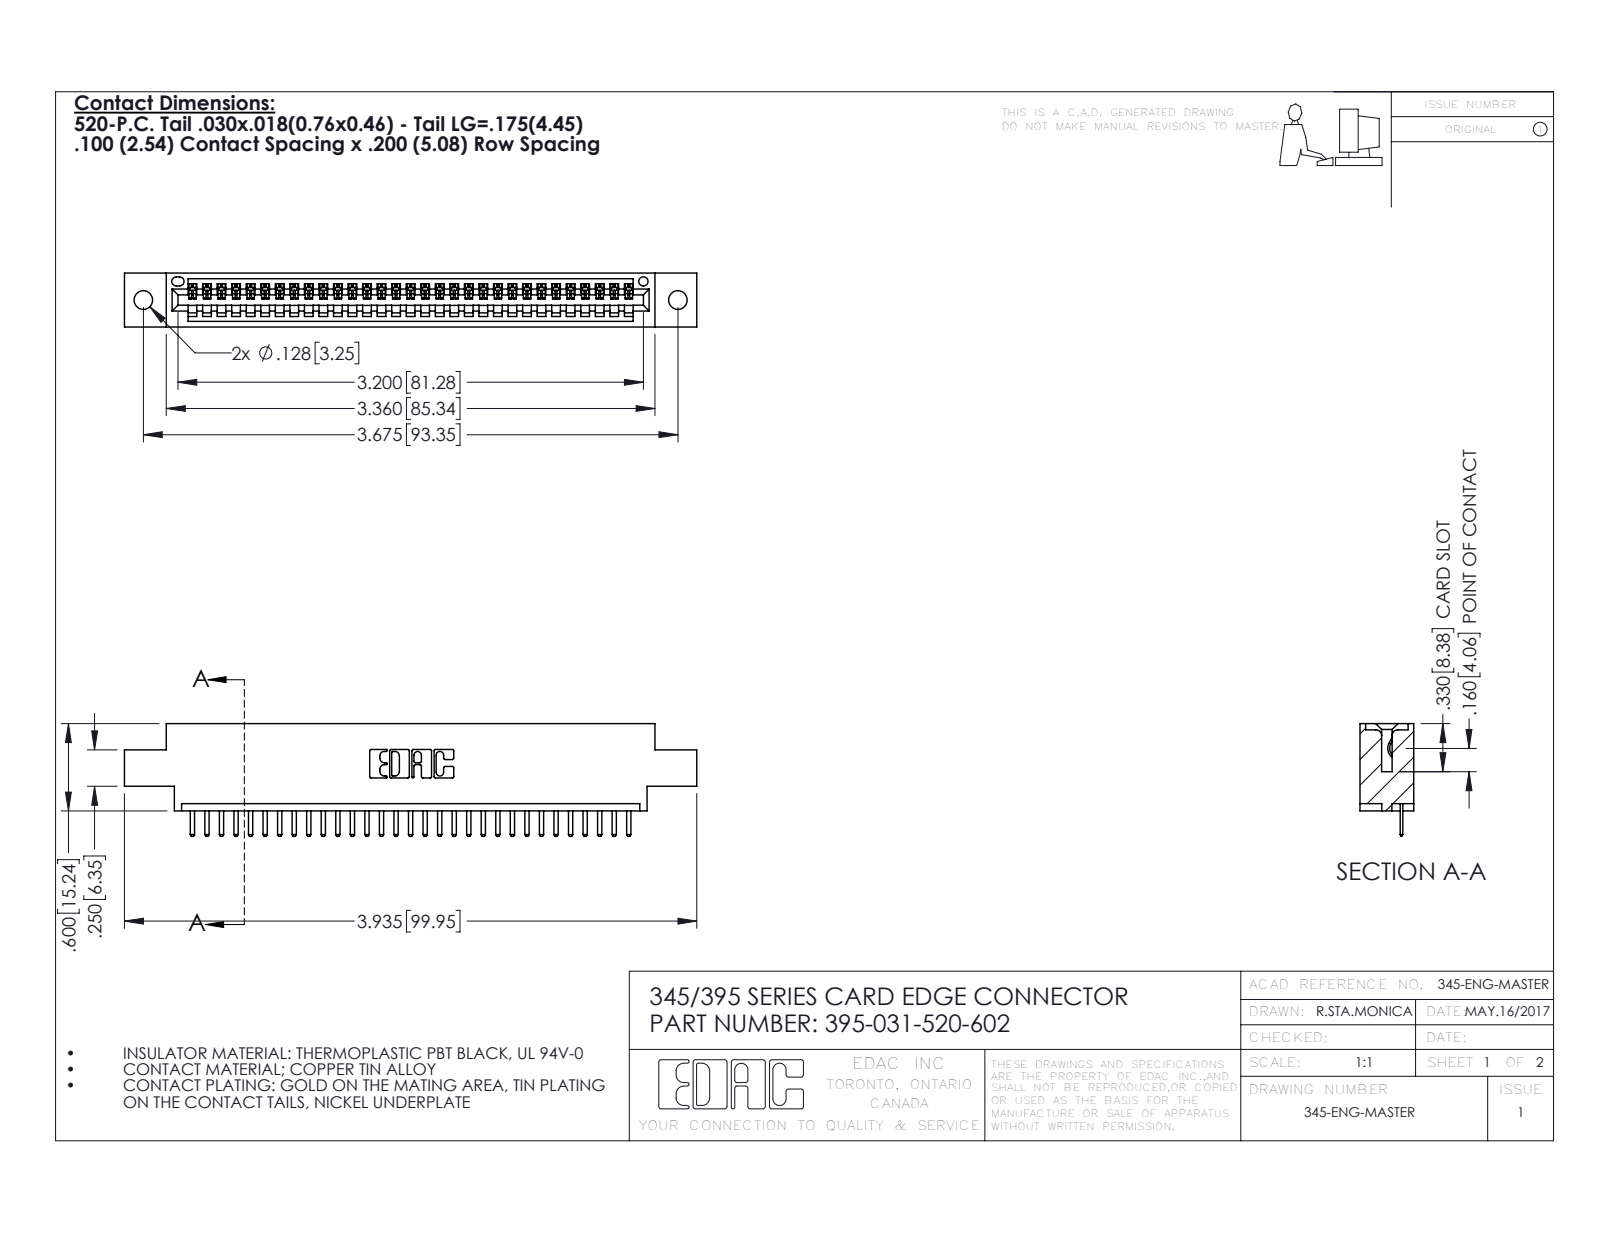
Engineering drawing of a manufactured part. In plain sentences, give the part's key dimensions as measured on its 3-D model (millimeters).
The part is named "345 Part_0.170 Offset - 0.128 Dia; 395-031-520-602; 345-292-001_345-293-120". Its 3-D file was written by "SolidWorks 2016 (CONFIG_CONTROL_DESIGN)". It is 32 solids with 2052 faces: 1386 planar, 666 cylindrical and 0 other. Overall it measures 99.9 by 19.7 by 9.4 millimeters. Its volume is 9 160 cubic millimeters and its surface area 11 590 square millimeters. Round holes: 2 of diameter 3.3, 1 of diameter 1.6. Partial cylindrical surfaces (rounded edges, fillets, slot ends): 64 of radius 0.3, 62 of radius 0.2, 22 of radius 0.3, 6 of radius 0.2, 6 of radius 0.8, 3 of radius 0.7, 2 of radius 0.8, 2 of radius 1. The main face-to-face distances are 7.6, 1.8, 9.4, 5.1, 2.5, 6.9, 0.6, 5.7, 1.8, 4.4. The hole center spacings are 6.9, 87.4, 93.3.
